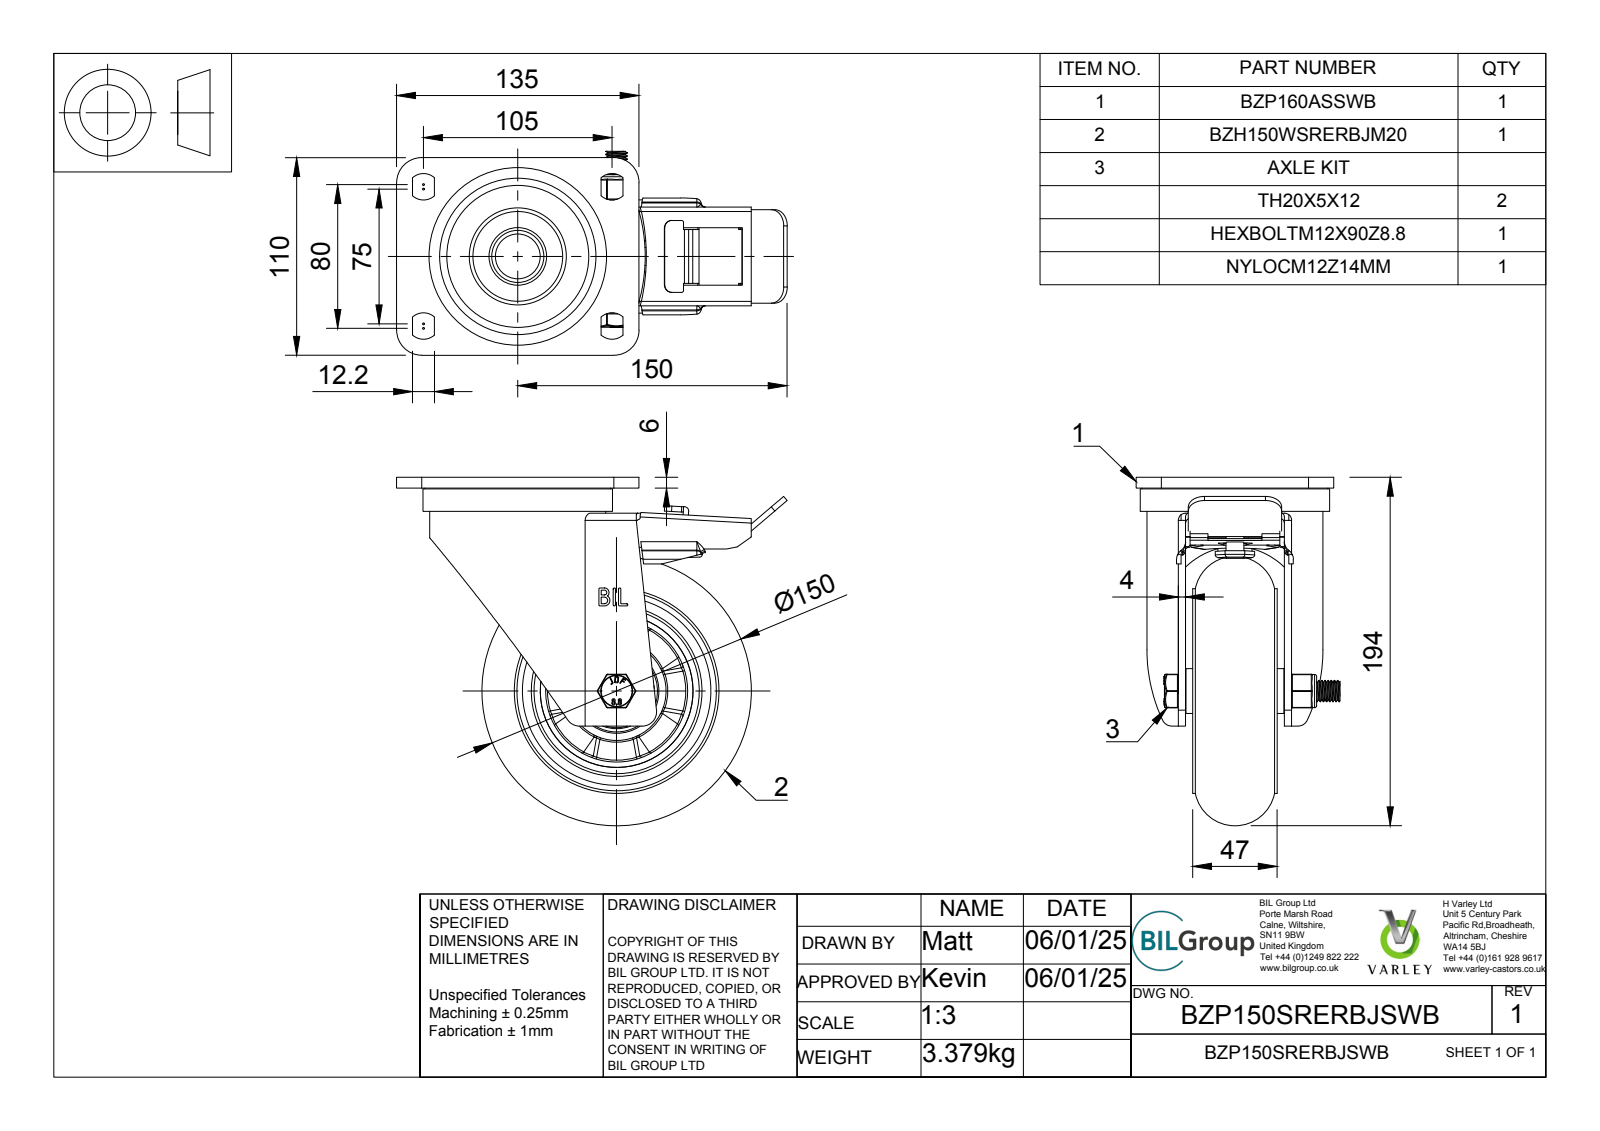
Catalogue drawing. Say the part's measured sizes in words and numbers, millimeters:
The part is named "BZP150SRERBJSWB v3; BZP160ASSWB - 55 v1; ZINC PLATED, PRESSED STEEL TOP PLATE; ZINC PLATED, PRESSED STEEL TOP PLATE Geometry (+8 more)". Its 3-D file was written by "Autodesk Translation Framework v13.20.0.188 (AP242_MANAGED_MODEL_BASED_3D_ENGINEERING_MIM_LF)". It is 42 solids with 1648 faces: 748 planar, 314 cylindrical and 586 other. Overall it measures 217.5 by 194 by 113.5 millimeters. Its volume is 891 848 cubic millimeters and its surface area 301 160 square millimeters. Round holes: 1 of diameter 5, 1 of diameter 10, 1 of diameter 12, 1 of diameter 12.2, 1 of diameter 12.5, 1 of diameter 14, 1 of diameter 19, 1 of diameter 20, 1 of diameter 28.5, 1 of diameter 30, 1 of diameter 30.8, 1 of diameter 40.3. Round bosses or shafts: 1 of diameter 114, 1 of diameter 105.5, 1 of diameter 98, 1 of diameter 95, 1 of diameter 83, 1 of diameter 55, 1 of diameter 50, 1 of diameter 40.8. Partial cylindrical surfaces (rounded edges, fillets, slot ends): 22 of radius 0.5, 9 of radius 1.5, 8 of radius 9.09, 6 of radius 2.5, 6 of radius 4, 5 of radius 1, 5 of radius 2, 4 of radius 0.47. The main face-to-face distances are 4, 2.5, 6.5, 6, 14, 3, 12.5, 59, 20, 5. The hole center spacings are 88.03.
